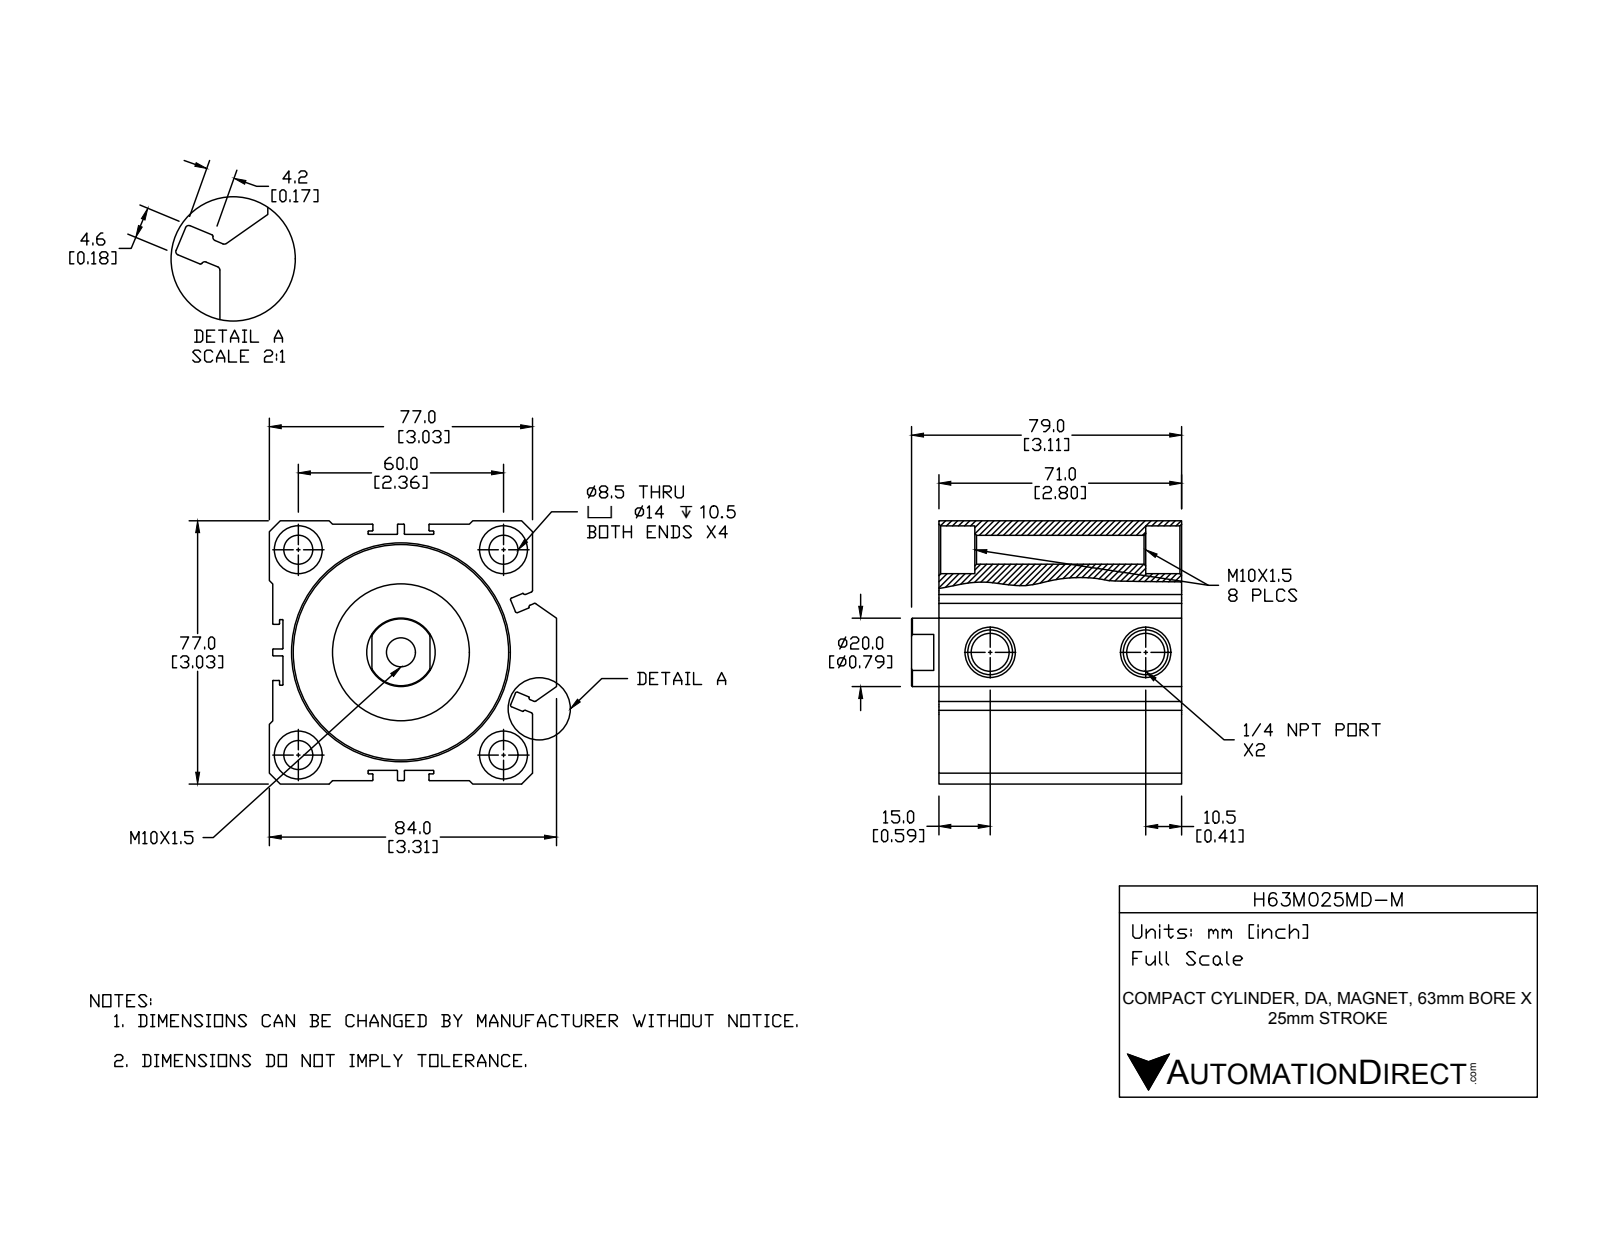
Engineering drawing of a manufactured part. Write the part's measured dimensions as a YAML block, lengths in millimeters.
part_name: "H63M025MD-M-BODY; H63M025MD-M-PISTON; H63M025MD-M"
step_written_by: "SolidWorks 2015 (CONFIG_CONTROL_DESIGN)"
units: millimeters
bodies: {solids: 2, faces: 255, planar: 99, cylindrical: 103, other: 53}
overall_size: [84, 79, 77]
volume: 294858
surface_area: 80992
round_holes:
  - {diameter: 8.5, count: 5}
  - {diameter: 14, count: 4}
  - {diameter: 11.13, count: 2}
  - {diameter: 20, count: 1}
  - {diameter: 45.51, count: 1}
  - {diameter: 63, count: 1}
round_bosses_or_shafts:
  - {diameter: 40, count: 1}
  - {diameter: 39, count: 1}
partial_cylinders:
  - {radius: 0.2, count: 40}
  - {radius: 0.5, count: 12}
face_to_face_distances: [1, 76, 77, 3, 4, 73, 23, 48.5, 69, 2]
hole_center_spacings: [42.43, 60, 84.85, 45.5]
